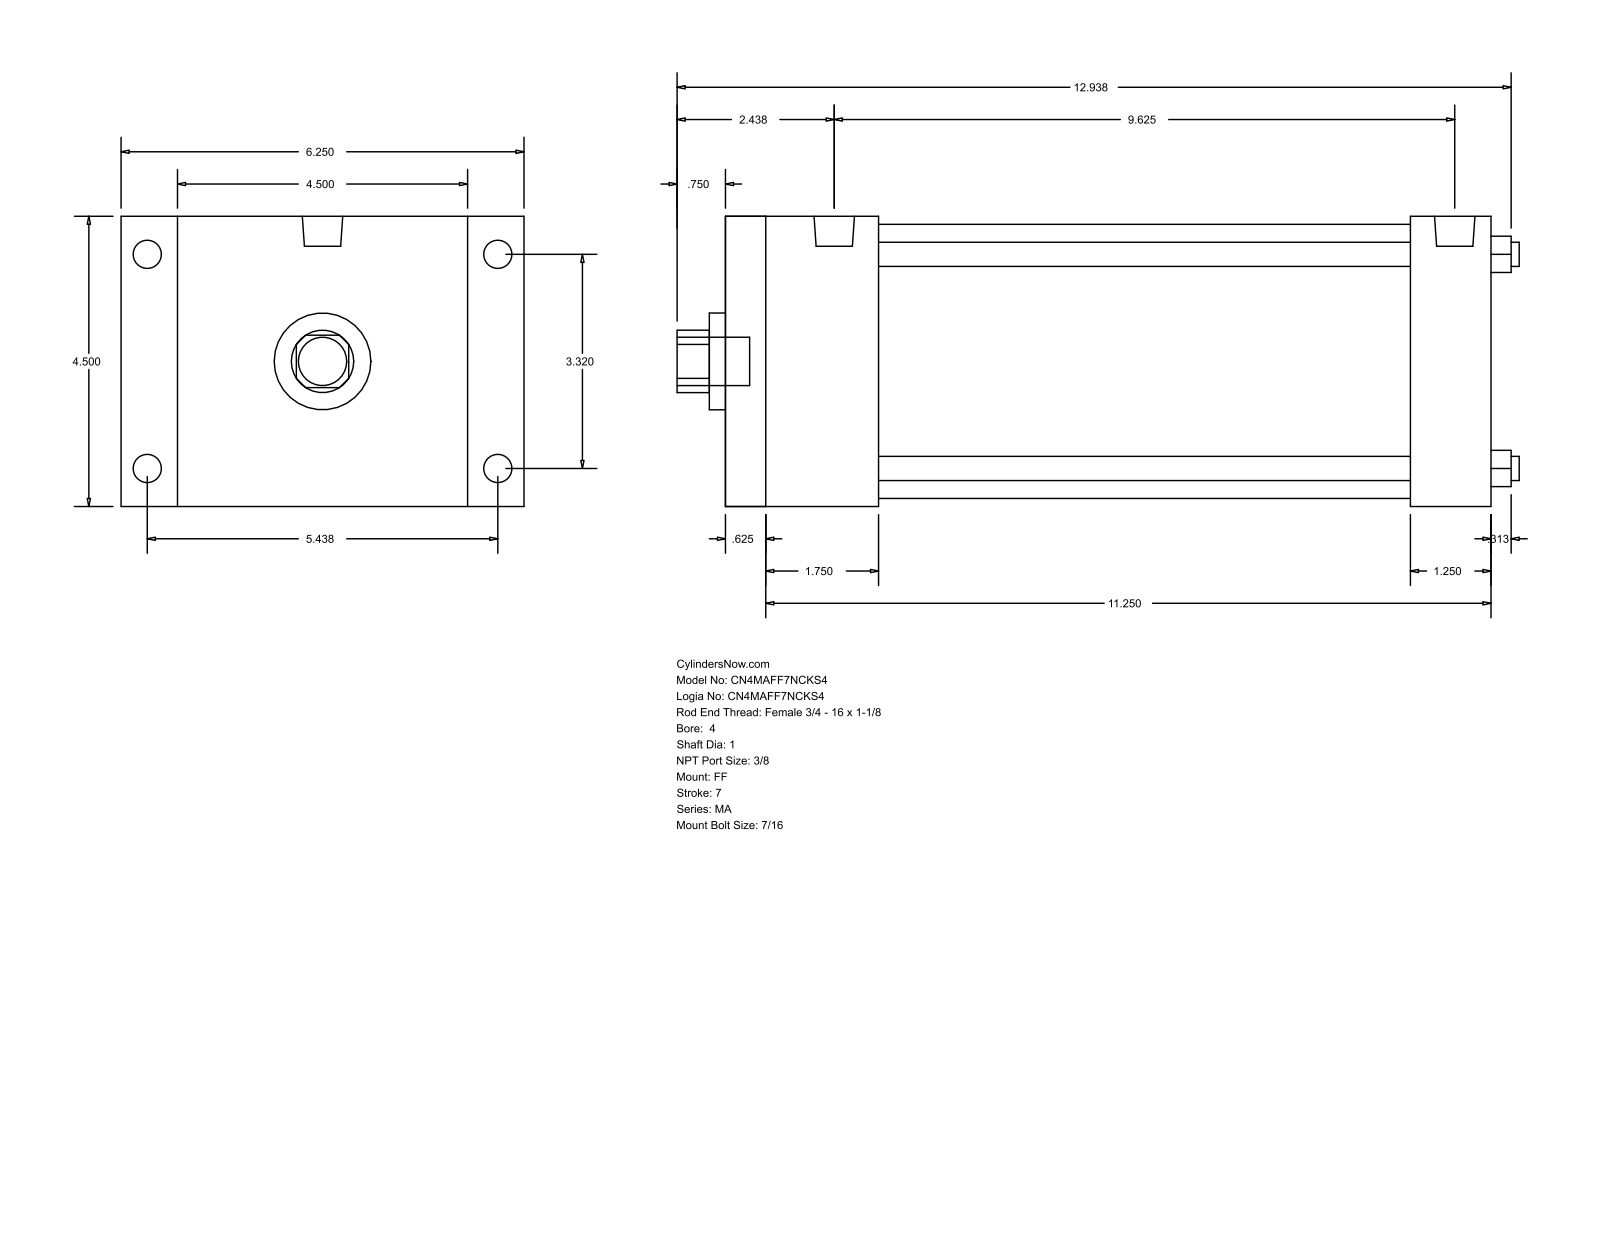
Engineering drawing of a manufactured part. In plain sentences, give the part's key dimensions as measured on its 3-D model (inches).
The part is named "MA_FF__0400_1". Its 3-D file was written by "GSSL Pune (CONFIG_CONTROL_DESIGN)". It is 0 solids with 92 faces: 64 planar, 28 cylindrical and 0 other. Overall it measures 13.063 by 6.25 by 4.5 inches. Round holes: 4 of diameter 0.375, 1 of diameter 1, 1 of diameter 1.5, 1 of diameter 4.25. Round bosses or shafts: 8 of diameter 0.437, 2 of diameter 0.627, 1 of diameter 0.75. Partial cylindrical surfaces (rounded edges, fillets, slot ends): 1 of radius 0.484. The main face-to-face distances are 4.5, 11.875, 0.625, 11.25, 0.875, 5.375, 10.625, 10, 1.25, 2.375. The hole center spacings are 2.347, 3.32, 4.695.
